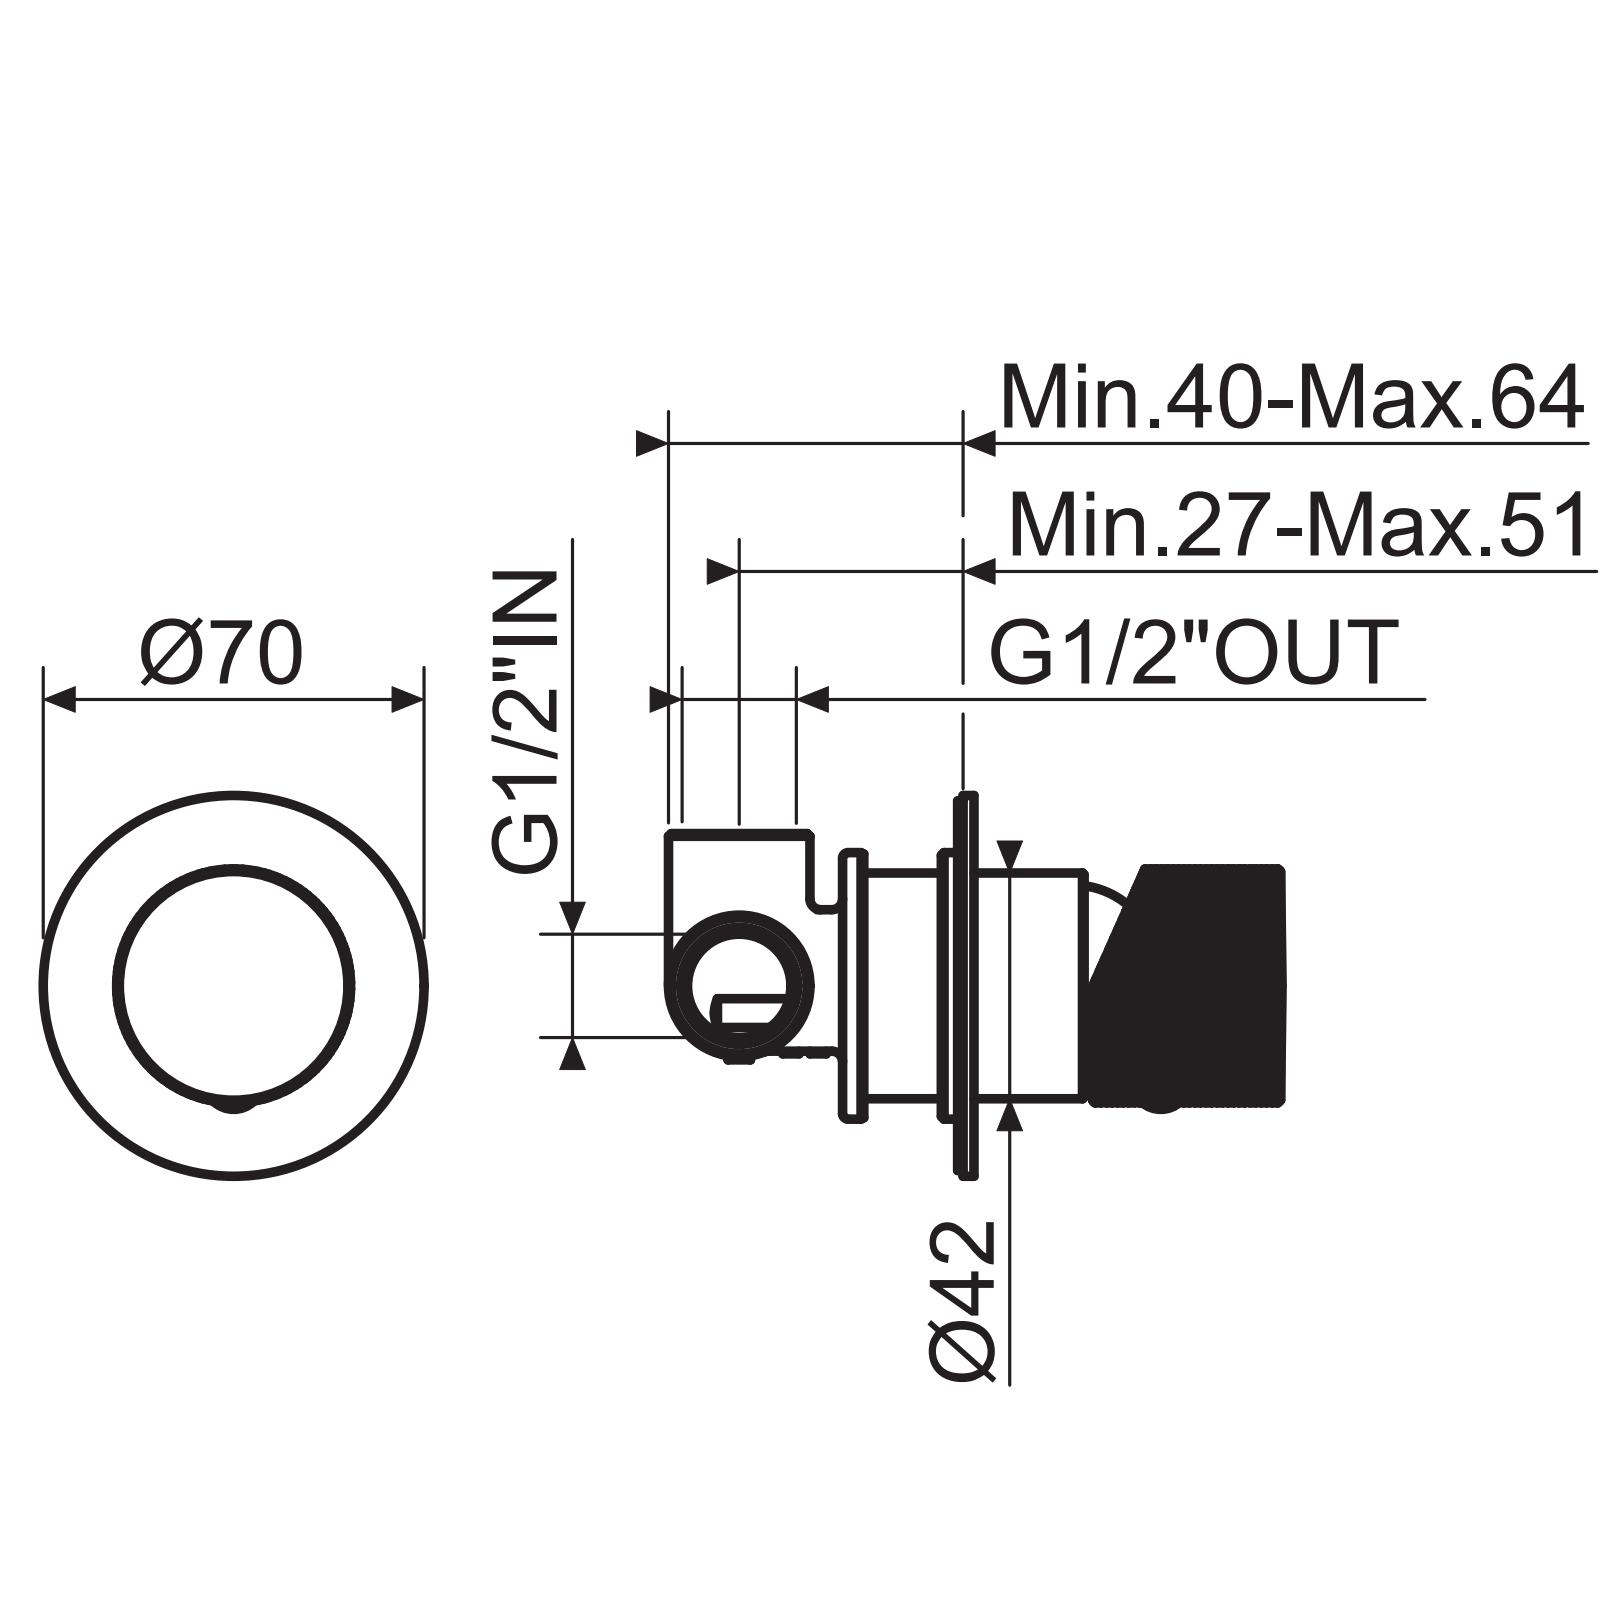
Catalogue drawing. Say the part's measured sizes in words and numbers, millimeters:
The part is named "SINMAC0010_AF0; ALOG230C001; AOTT608C002_AF0; ALOG230W001_AF0 (+4 more)". Its 3-D file was written by "CREO PARAMETRIC BY PTC INC, 2022164 (CONFIG_CONTROL_DESIGN)". It is 6 solids with 5285 faces: 2113 planar, 1098 cylindrical and 2074 other. Overall it measures 70 by 70 by 59.11 millimeters. Its volume is 24 539 cubic millimeters and its surface area 28 980 square millimeters. Round holes: 1 of diameter 4.2, 1 of diameter 5, 1 of diameter 5.1, 1 of diameter 6.5, 1 of diameter 8, 1 of diameter 10.3, 1 of diameter 27.7, 1 of diameter 32, 1 of diameter 37.5, 1 of diameter 38, 1 of diameter 40, 1 of diameter 46.5. Round bosses or shafts: 1 of diameter 70, 1 of diameter 49, 1 of diameter 43, 1 of diameter 41.5, 1 of diameter 36.8, 1 of diameter 16. Partial cylindrical surfaces (rounded edges, fillets, slot ends): 16 of radius 0.1, 2 of radius 2.5. The main face-to-face distances are 2, 55.85, 53.85, 29.84, 0.47, 2.47, 56.32, 29.86, 22.72, 22.25.
